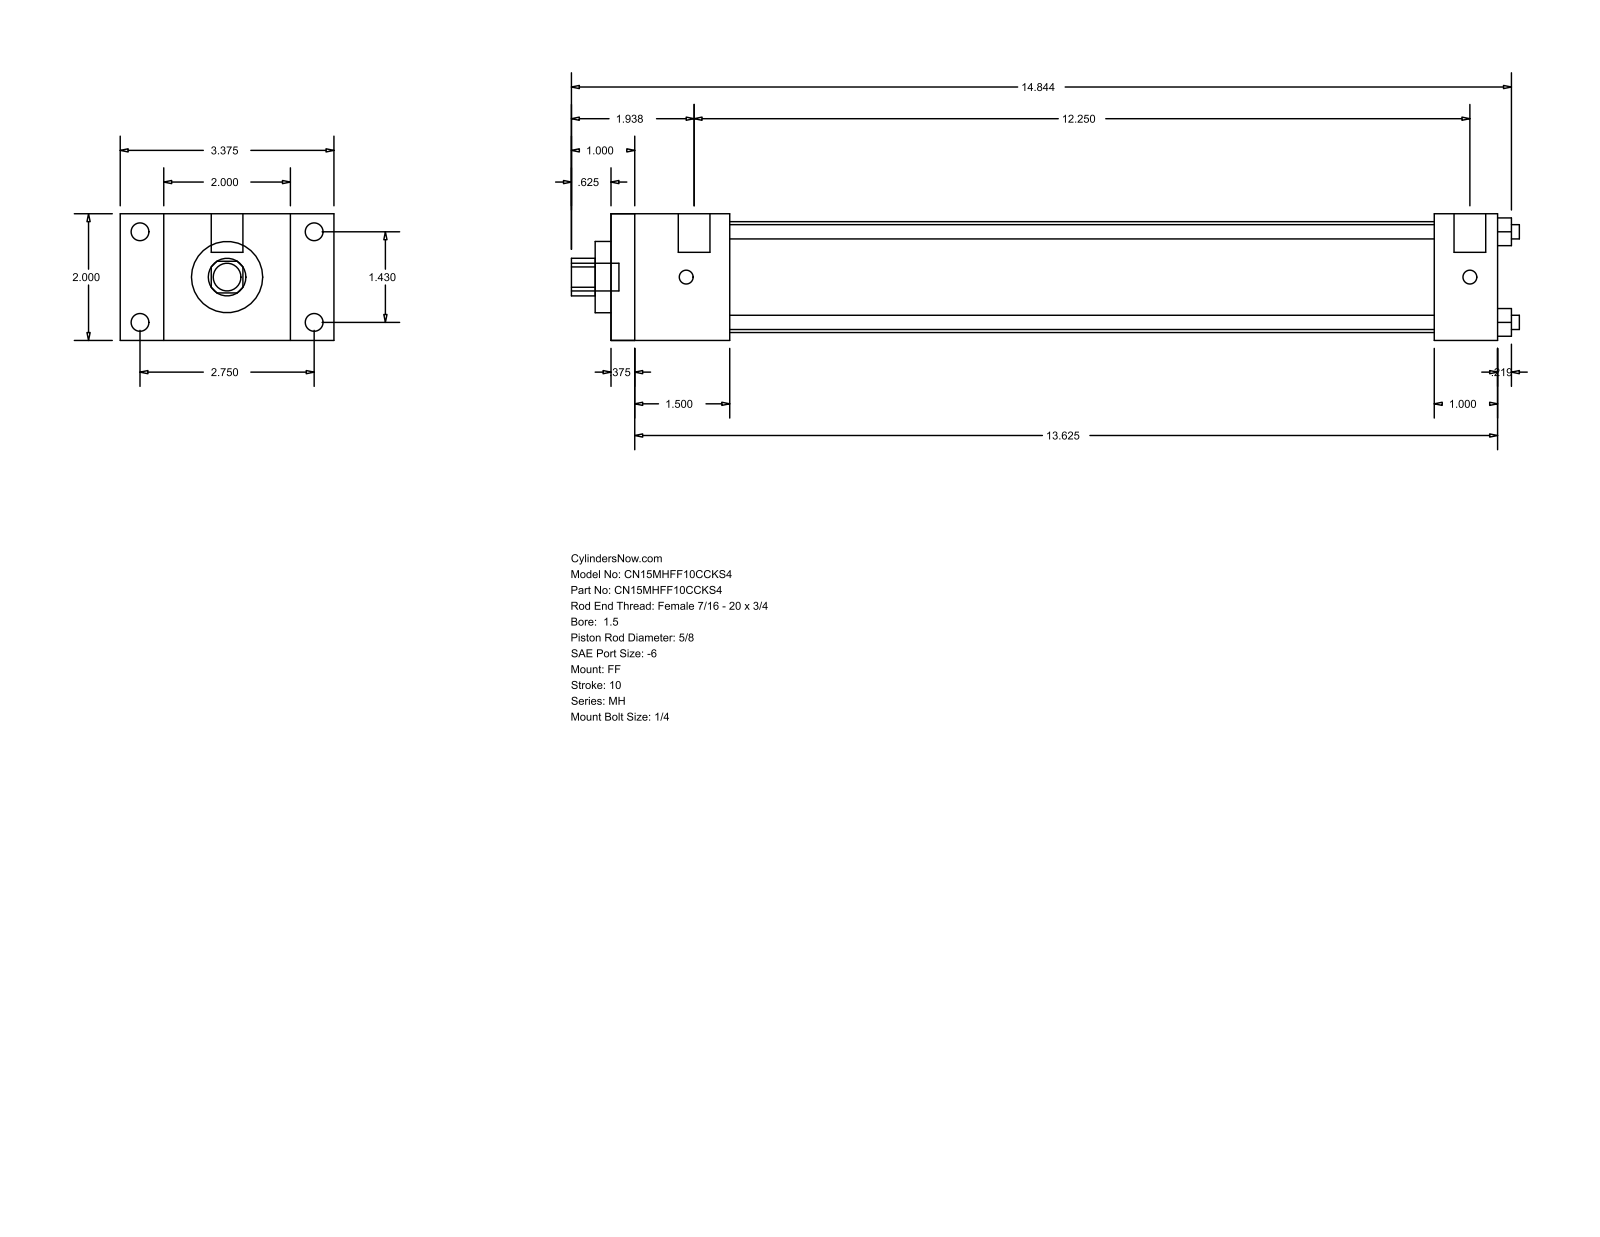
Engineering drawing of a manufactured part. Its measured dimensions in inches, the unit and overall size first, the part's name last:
Units: inches
Overall size (bounding box): 14.969 × 3.375 × 2
Round holes (diameter × count): ⌀0.225 ×4, ⌀0.625 ×1, ⌀1.125 ×1, ⌀1.75 ×1
Round bosses / shafts (diameter × count): ⌀0.281 ×4, ⌀0.219 ×4, ⌀0.5 ×2, ⌀0.437 ×1
Partial cylindrical surfaces — rounded edges, fillets, slot ends (radius × count): R0.297 ×1
Main face-to-face distances: 2, 14, 0.375, 13.625, 0.687, 2.687, 1.875, 1.5, 12.125, 13
Hole centre spacings: 1.011, 1.43, 2.022
Bodies: 0 solids, 92 faces (64 planar, 28 cylindrical, 0 other)
Part name (STEP PRODUCT): MH_FF__0150_0.625
STEP written by: GSSL Pune (CONFIG_CONTROL_DESIGN)
